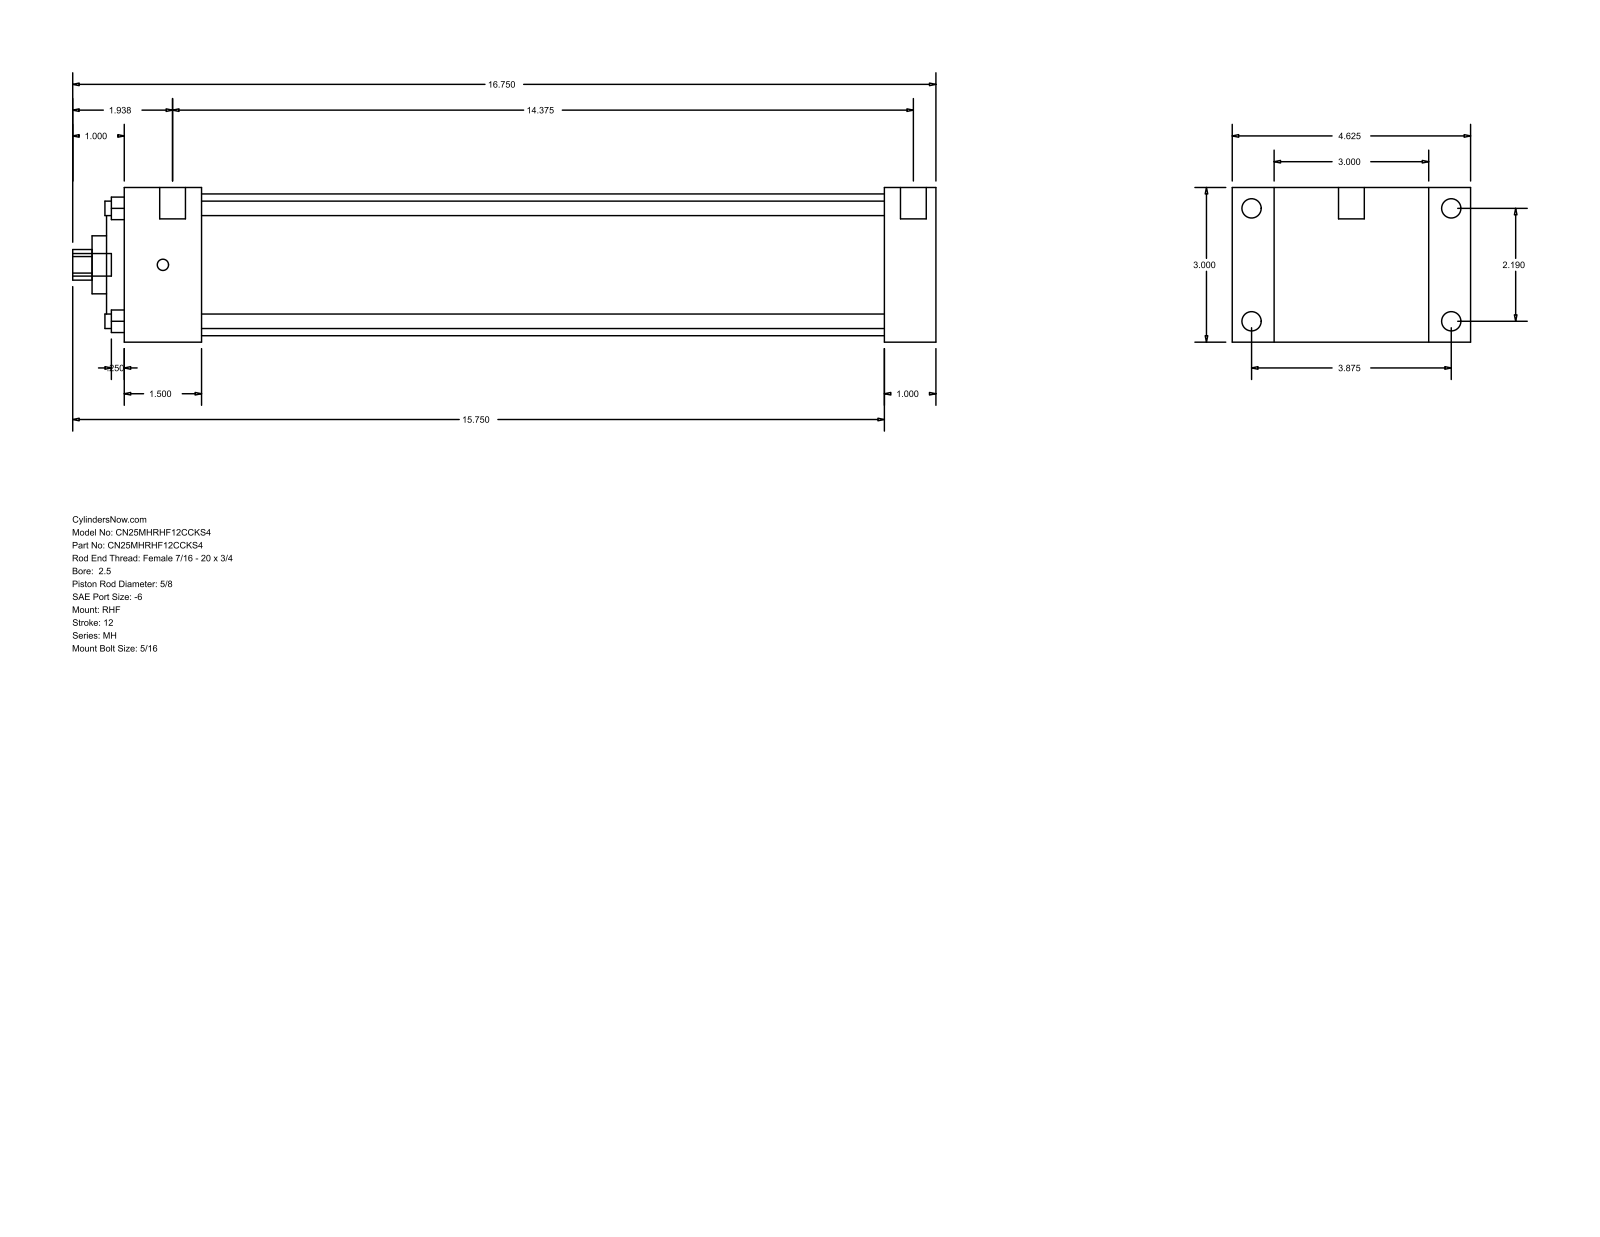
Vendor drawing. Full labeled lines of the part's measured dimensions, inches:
Part name (STEP PRODUCT): MH_RHF__0250_0.625
STEP written by: GSSL Pune (CONFIG_CONTROL_DESIGN)
Units: inches
Bodies: 0 solids, 90 faces (61 planar, 29 cylindrical, 0 other)
Overall size (bounding box): 16.75 × 4.625 × 3
Round holes (diameter × count): ⌀0.281 ×4, ⌀0.625 ×1, ⌀1.125 ×1, ⌀2.187 ×1, ⌀2.75 ×1
Round bosses / shafts (diameter × count): ⌀0.375 ×4, ⌀0.219 ×4, ⌀0.5 ×2, ⌀0.437 ×1
Partial cylindrical surfaces — rounded edges, fillets, slot ends (radius × count): R0.297 ×1
Main face-to-face distances: 3, 1, 0.813, 3.813, 15.75, 14.75, 4.625, 1.5, 13.25, 14.25
Hole centre spacings: 1.548, 2.19, 3.097
